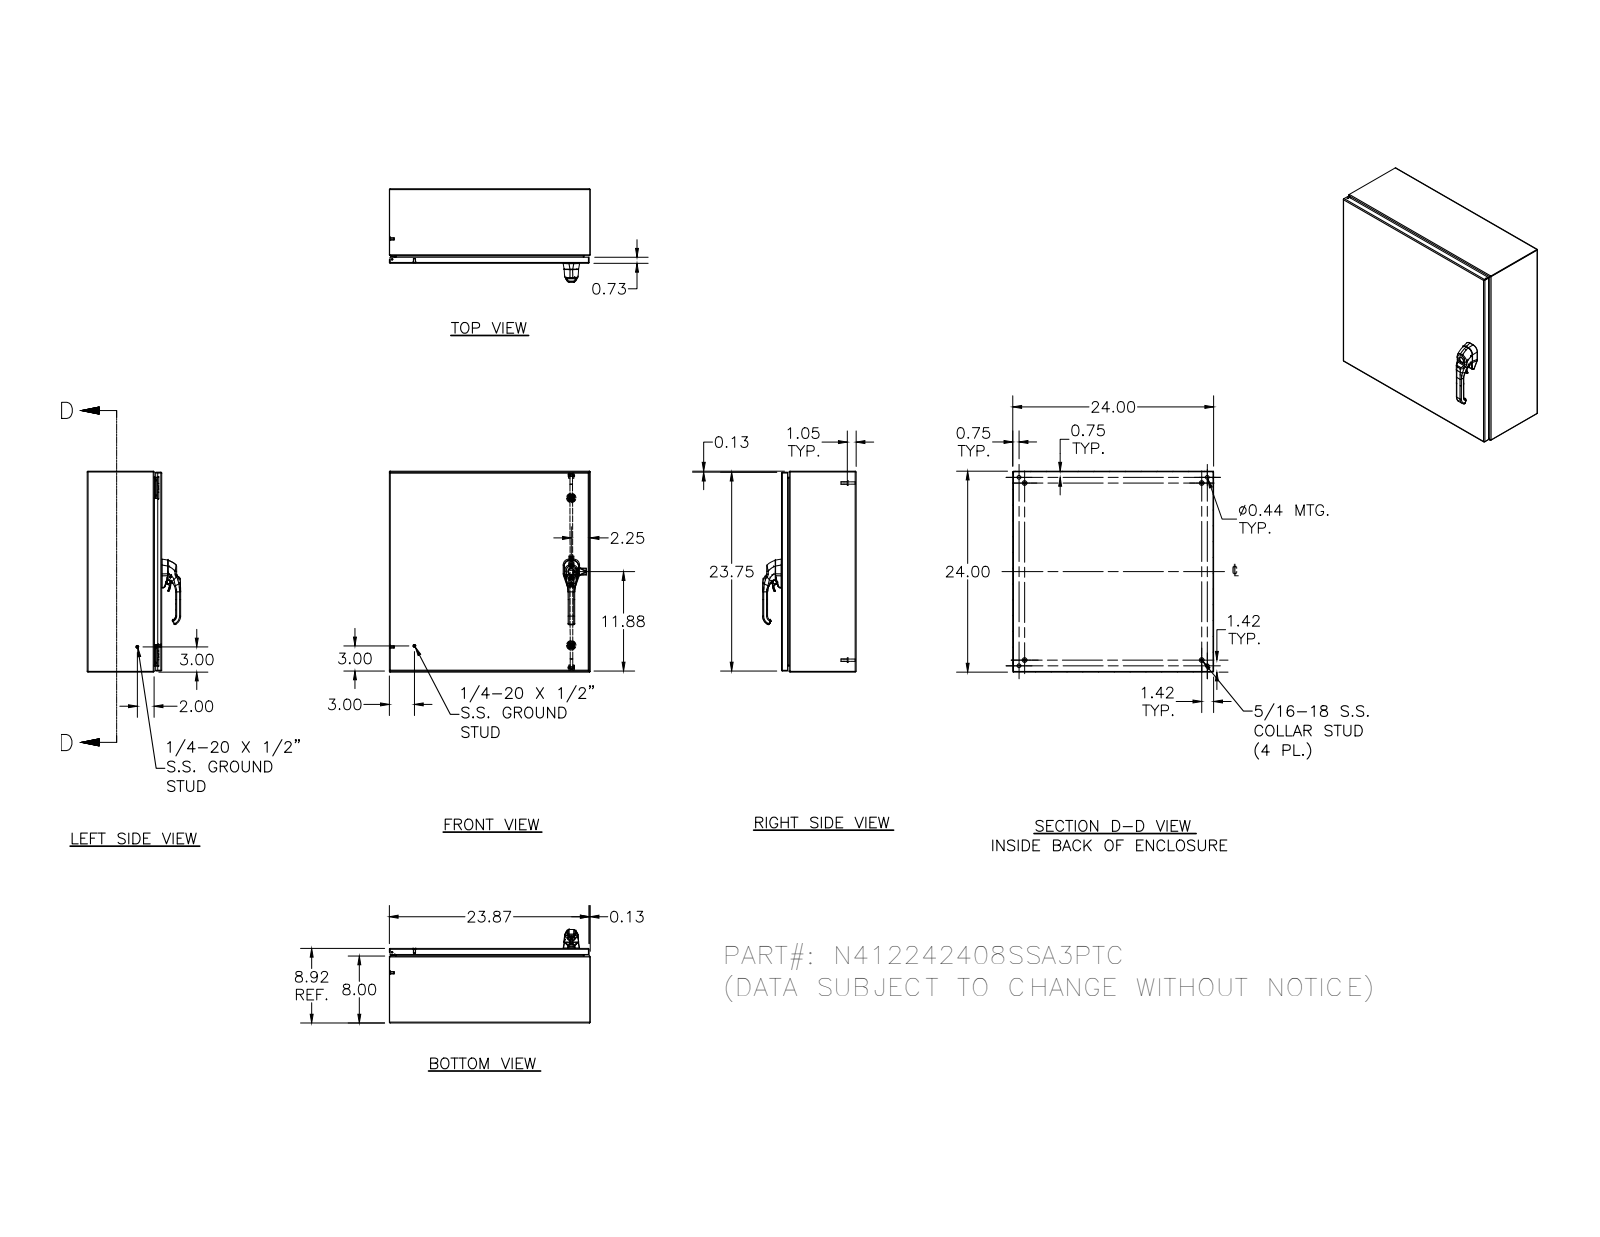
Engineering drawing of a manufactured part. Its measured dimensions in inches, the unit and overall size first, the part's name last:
Units: inches
Overall size (bounding box): 24 × 24 × 11.166
Round holes (diameter × count): ⌀0.165 ×5, ⌀0.188 ×5, ⌀0.093 ×4, ⌀0.152 ×4, ⌀0.167 ×4, ⌀0.172 ×4, ⌀0.197 ×4, ⌀0.437 ×4, ⌀0.213 ×3, ⌀0.106 ×2, ⌀0.156 ×2, ⌀0.16 ×2
Round bosses / shafts (diameter × count): ⌀0.25 ×10, ⌀0.236 ×6, ⌀0.591 ×5, ⌀0.563 ×4, ⌀0.36 ×4, ⌀0.32 ×4, ⌀0.31 ×4, ⌀0.3 ×4
Partial cylindrical surfaces — rounded edges, fillets, slot ends (radius × count): R0.02 ×180, R0.012 ×101, R0.031 ×30, R0.05 ×26, R0.118 ×23, R0.019 ×21, R0.105 ×20, R0.016 ×18
Main face-to-face distances: 0.074, 8.843, 23.926, 8.917, 8.769, 23.852, 24, 7.926, 0.917, 0.739
Hole centre spacings: 19.996, 22.5, 22.869, 0.017, 0.66, 1.618, 20.656, 23.418
Volume: 166.9 in³ · Surface area: 4 387 in²
Bodies: 63 solids, 3088 faces (1046 planar, 1119 cylindrical, 923 other)
Part name (STEP PRODUCT): N412242408SSA3PTC; N412242408SSA3PTCBKP; N4122424SSA3PTCLID; HFW328176 (+8 more)
STEP written by: Autodesk Inventor 2011 (AUTOMOTIVE_DESIGN)
